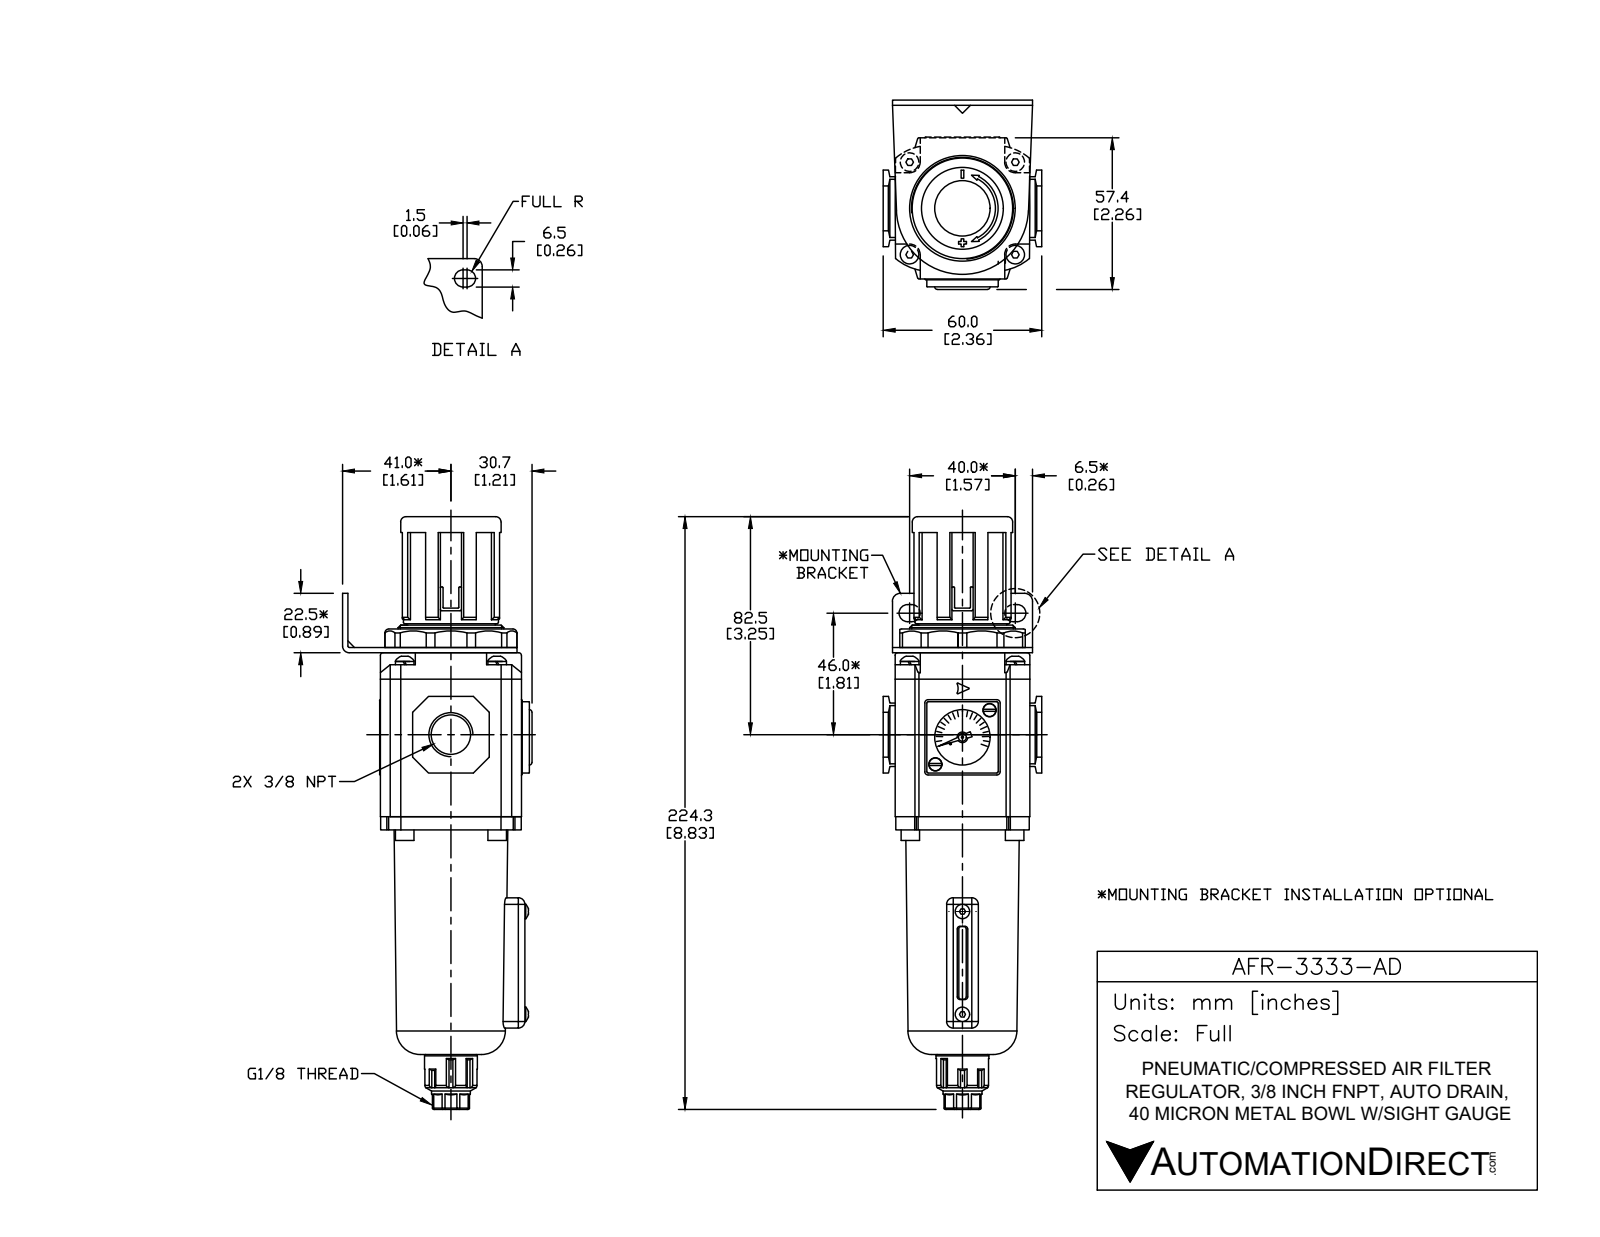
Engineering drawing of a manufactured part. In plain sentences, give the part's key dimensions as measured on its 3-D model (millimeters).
The part is named "AFR-3333-AD". Its 3-D file was written by "SolidWorks 2015 (CONFIG_CONTROL_DESIGN)". It is 16 solids with 686 faces: 418 planar, 181 cylindrical and 87 other. Overall it measures 224.3 by 72 by 60 millimeters. Its volume is 358 978 cubic millimeters and its surface area 64 781 square millimeters. Round holes: 6 of diameter 3, 1 of diameter 2, 1 of diameter 6.2, 1 of diameter 14.27, 1 of diameter 21, 1 of diameter 30, 1 of diameter 32. Round bosses or shafts: 6 of diameter 5.5, 4 of diameter 7, 2 of diameter 2.7, 1 of diameter 40, 1 of diameter 38, 1 of diameter 36, 1 of diameter 33.5, 1 of diameter 20.46. Partial cylindrical surfaces (rounded edges, fillets, slot ends): 16 of radius 1, 10 of radius 1.2, 8 of radius 1.3, 8 of radius 2.5, 8 of radius 9.5, 8 of radius 19.9, 6 of radius 0.5, 6 of radius 3.25. The main face-to-face distances are 2, 62, 64, 53.4, 51, 1, 55.5, 52.4, 67, 4.5. The hole center spacings are 26.58, 14.5, 35, 40, 53.15, 28.99.
